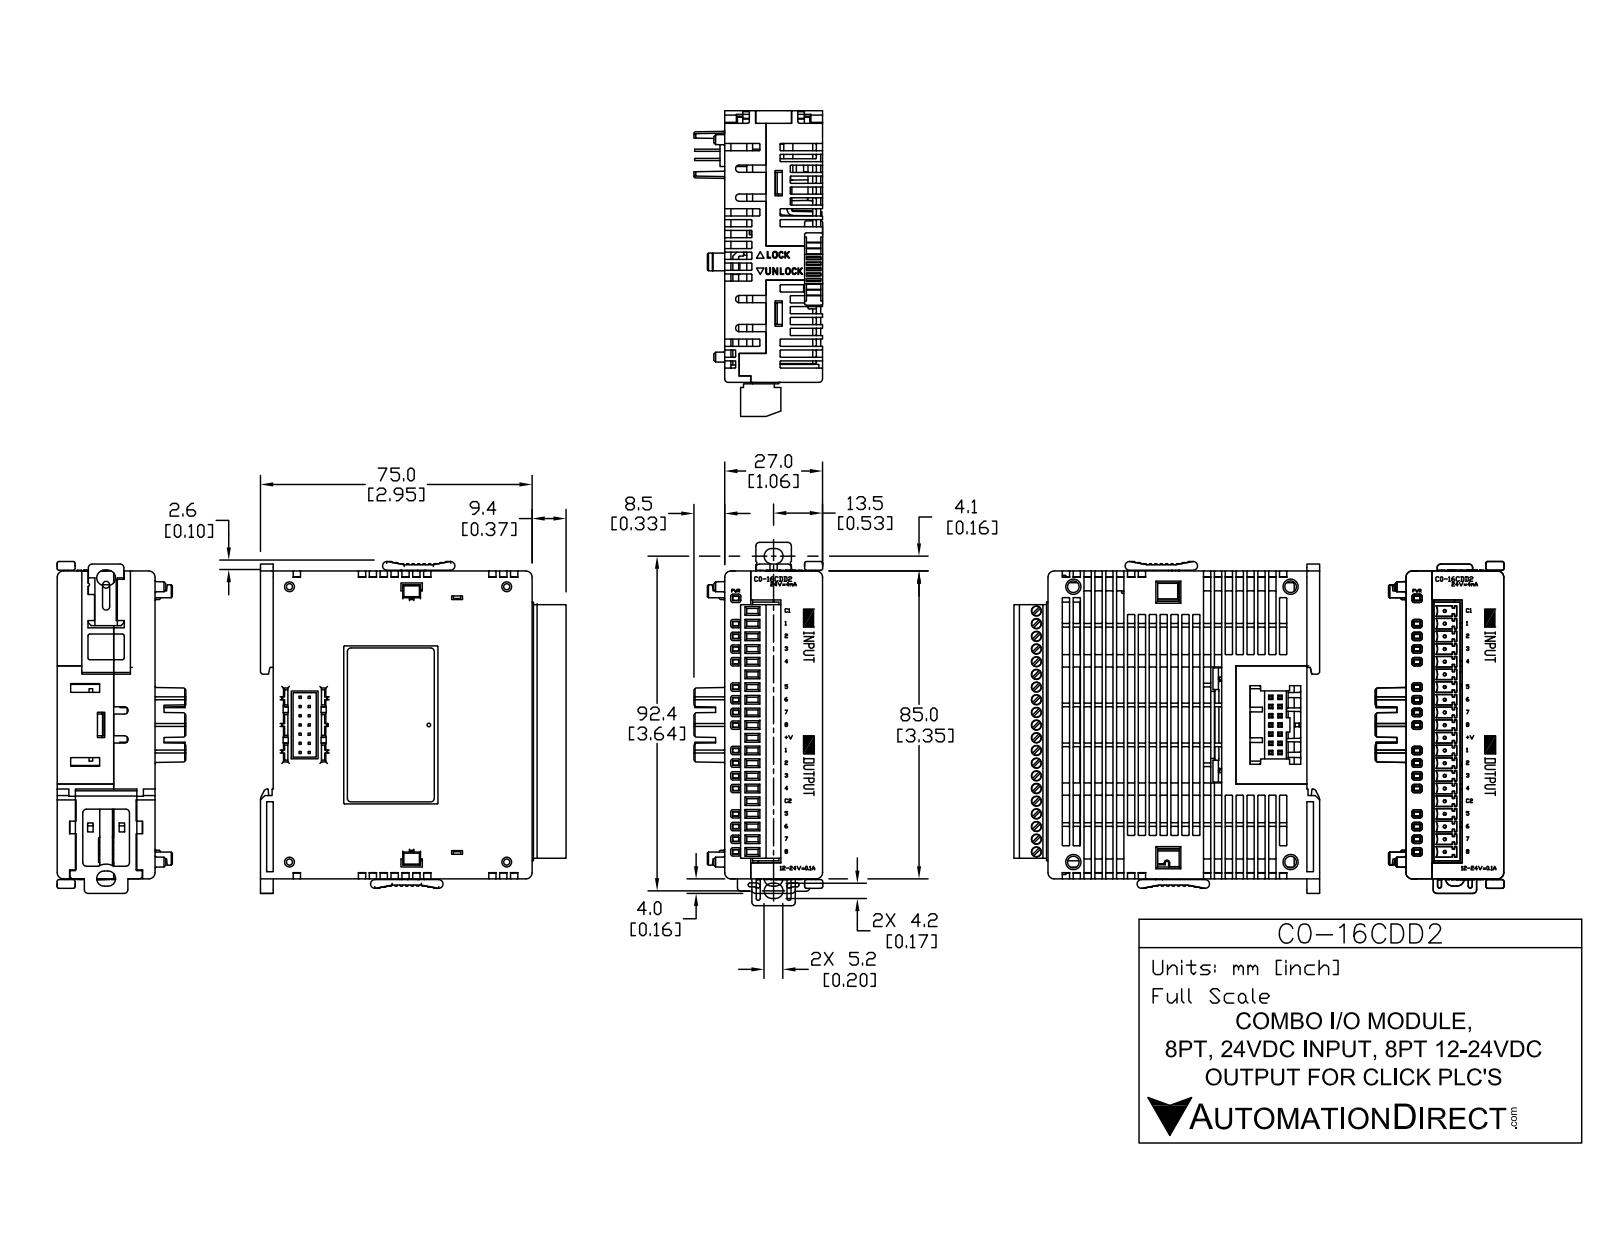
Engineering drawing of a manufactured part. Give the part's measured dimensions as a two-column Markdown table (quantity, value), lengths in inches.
| quantity | value |
| --- | --- |
| part name | C0-16CDD2 |
| STEP written by | SolidWorks 2017 (AUTOMOTIVE_DESIGN) |
| units | inches |
| bodies | 1 solid, 4093 faces (2884 planar, 1037 cylindrical, 172 other) |
| overall size | 3.606 × 3.323 × 1.4 |
| volume | 10.07 in³ |
| surface area | 52.13 in² |
| round holes (diameter × count) | 0.039 × 20, 0.11 × 20, 0.126 × 4, 0.079 × 2 |
| round bosses / shafts (diameter × count) | 0.102 × 20, 0.075 × 1 |
| partial cylindrical surfaces (radius × count) | 0.008 × 570, 0.02 × 43, 0.012 × 22, 0.11 × 20, 0.039 × 18, 0.047 × 12, 0.067 × 6, 0.083 × 4 |
| main face-to-face distances | 0.02, 1.063, 0.02, 1.043, 2.815, 3.346, 0.067, 1.035, 1.056, 0.138 |
| hole center spacings | 0.138, 0.276, 0.413, 0.551, 0.689, 0.827, 0.965, 1.102 |
